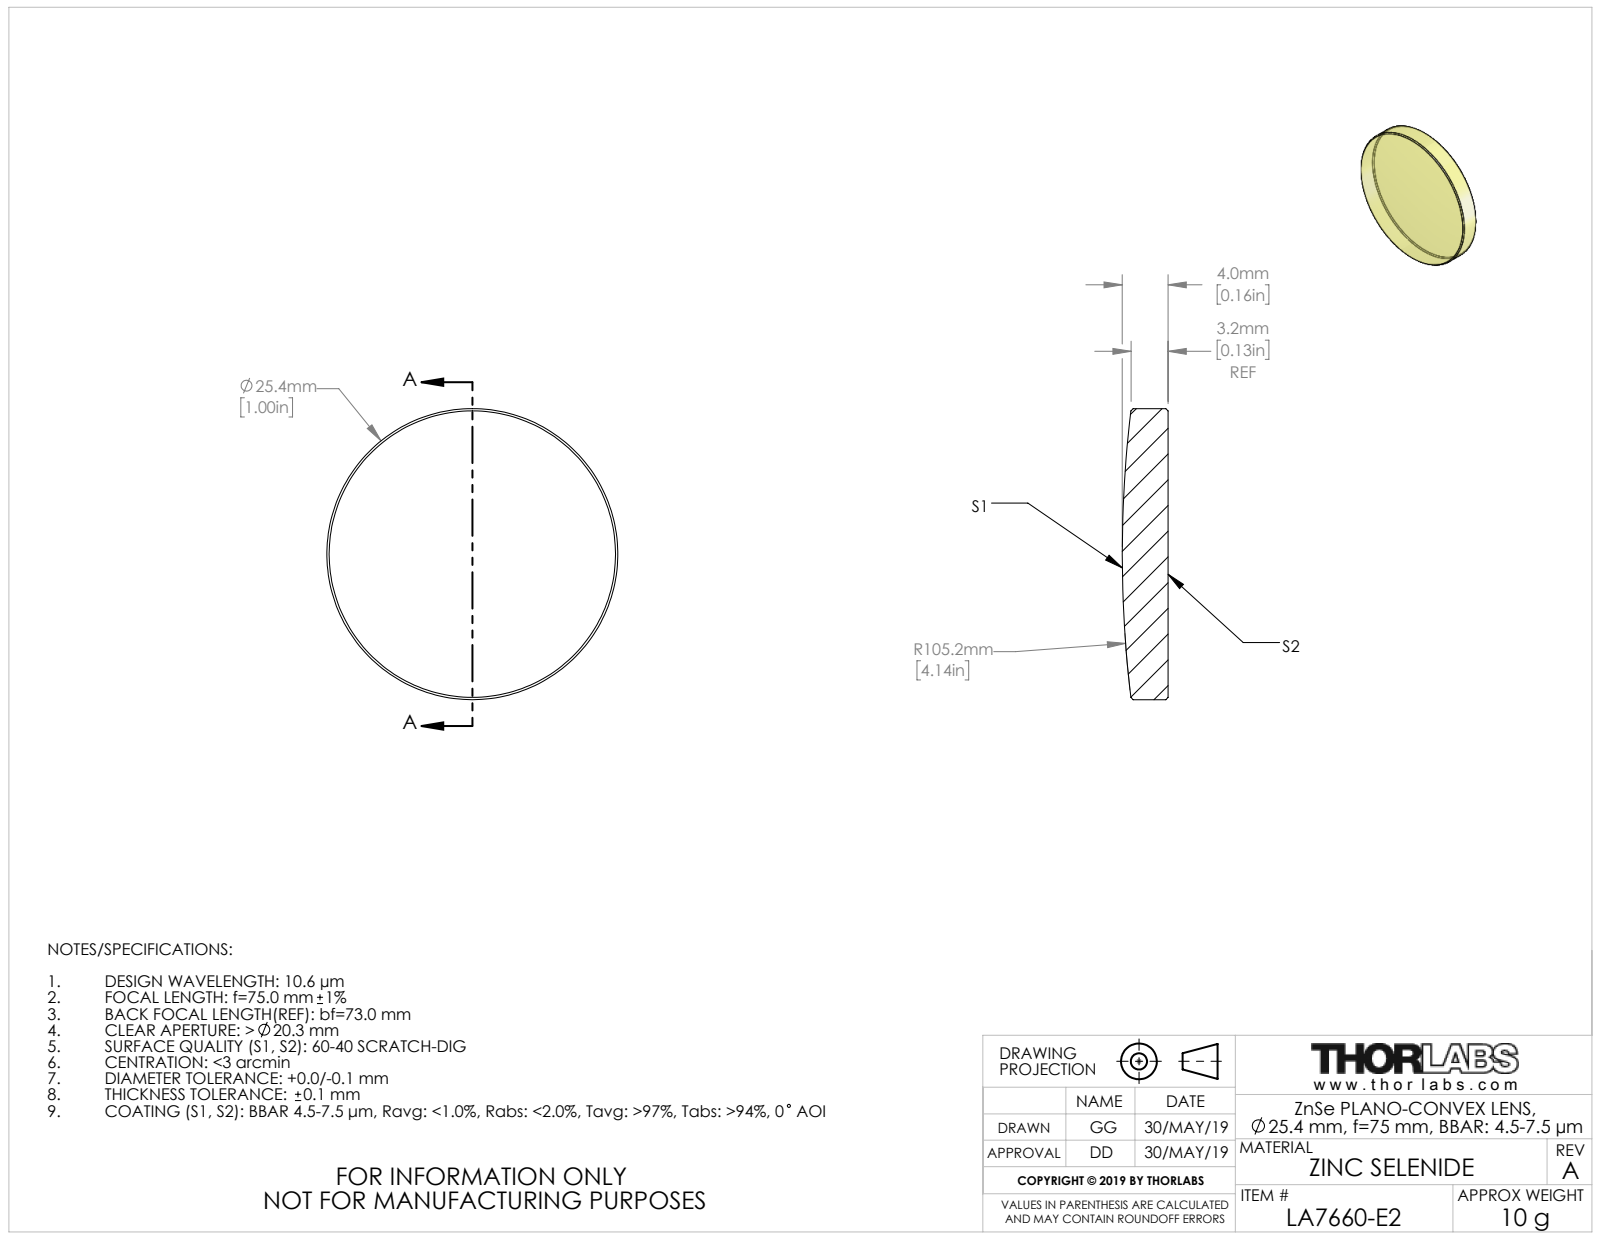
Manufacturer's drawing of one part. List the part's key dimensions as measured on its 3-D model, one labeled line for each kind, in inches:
Part name (STEP PRODUCT): TTN047594-E0W
STEP written by: SolidWorks 2018 (CONFIG_CONTROL_DESIGN)
Units: inches
Bodies: 1 solid, 9 faces (1 planar, 2 cylindrical, 6 other)
Overall size (bounding box): 1 × 1 × 0.157
Volume: 0.112 in³ · Surface area: 1.947 in²
Round bosses / shafts (diameter × count): ⌀1 ×1
